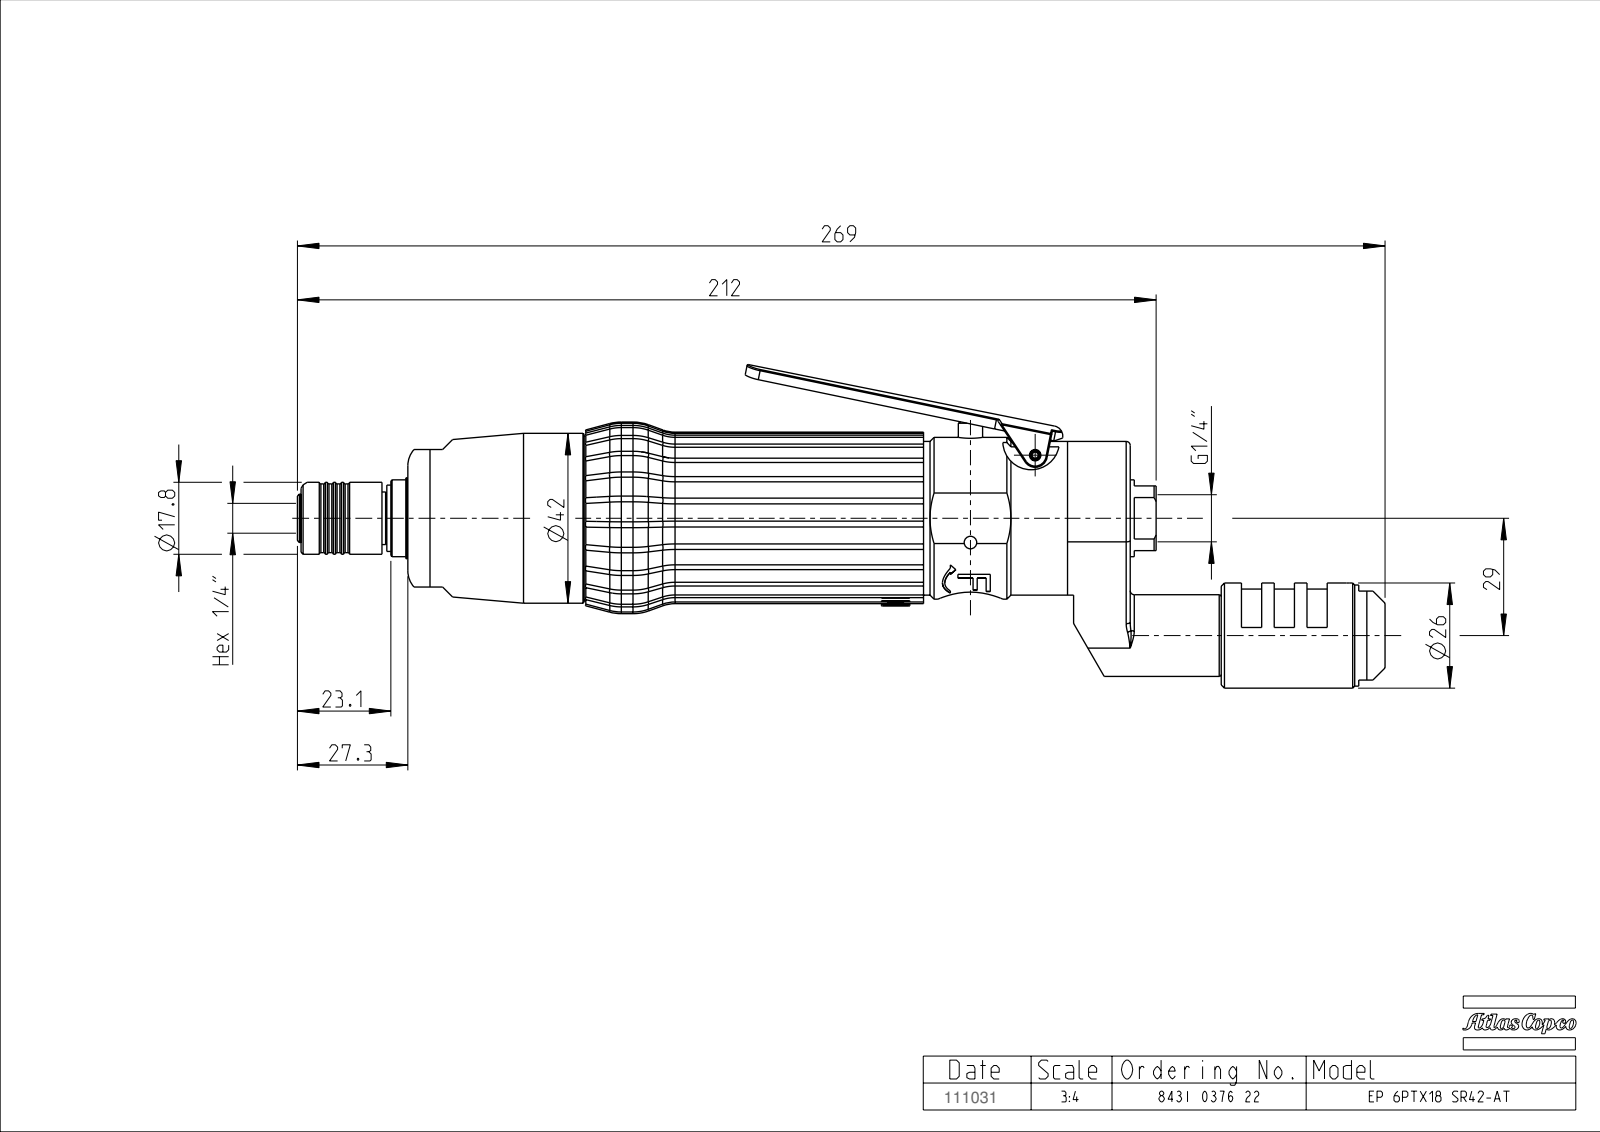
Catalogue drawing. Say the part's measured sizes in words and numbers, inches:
The part is named "EXT_COMP_SW0003". Its 3-D file was written by "CREO PARAMETRIC BY PTC INC, 2020281 (CONFIG_CONTROL_DESIGN)". It is 2 solids with 871 faces: 184 planar, 281 cylindrical and 406 other. Overall it measures 10.598 by 2.378 by 2.174 inches. Its volume is 16.63 cubic inches and its surface area 67.47 square inches. Round holes: 2 of diameter 0.067, 1 of diameter 0.059, 1 of diameter 0.11, 1 of diameter 0.122, 1 of diameter 0.185, 1 of diameter 0.386, 1 of diameter 0.459, 1 of diameter 0.488, 1 of diameter 0.61, 1 of diameter 0.724. Round bosses or shafts: 2 of diameter 0.591, 1 of diameter 1.654, 1 of diameter 1.575, 1 of diameter 1.496, 1 of diameter 1.024, 1 of diameter 0.984, 1 of diameter 0.906, 1 of diameter 0.795. Partial cylindrical surfaces (rounded edges, fillets, slot ends): 97 of radius 0.039, 6 of radius 0.02, 6 of radius 0.138, 4 of radius 0.012, 2 of radius 0.157, 1 of radius 0.118, 1 of radius 0.128, 1 of radius 0.236. The main face-to-face distances are 1.594, 3.043, 0.039, 0.079, 1.496, 0.551, 0.252, 7.031, 1.417, 7.283. The hole center spacings are 0.32, 0.154, 1.058, 1.142, 1.356, 1.437.
